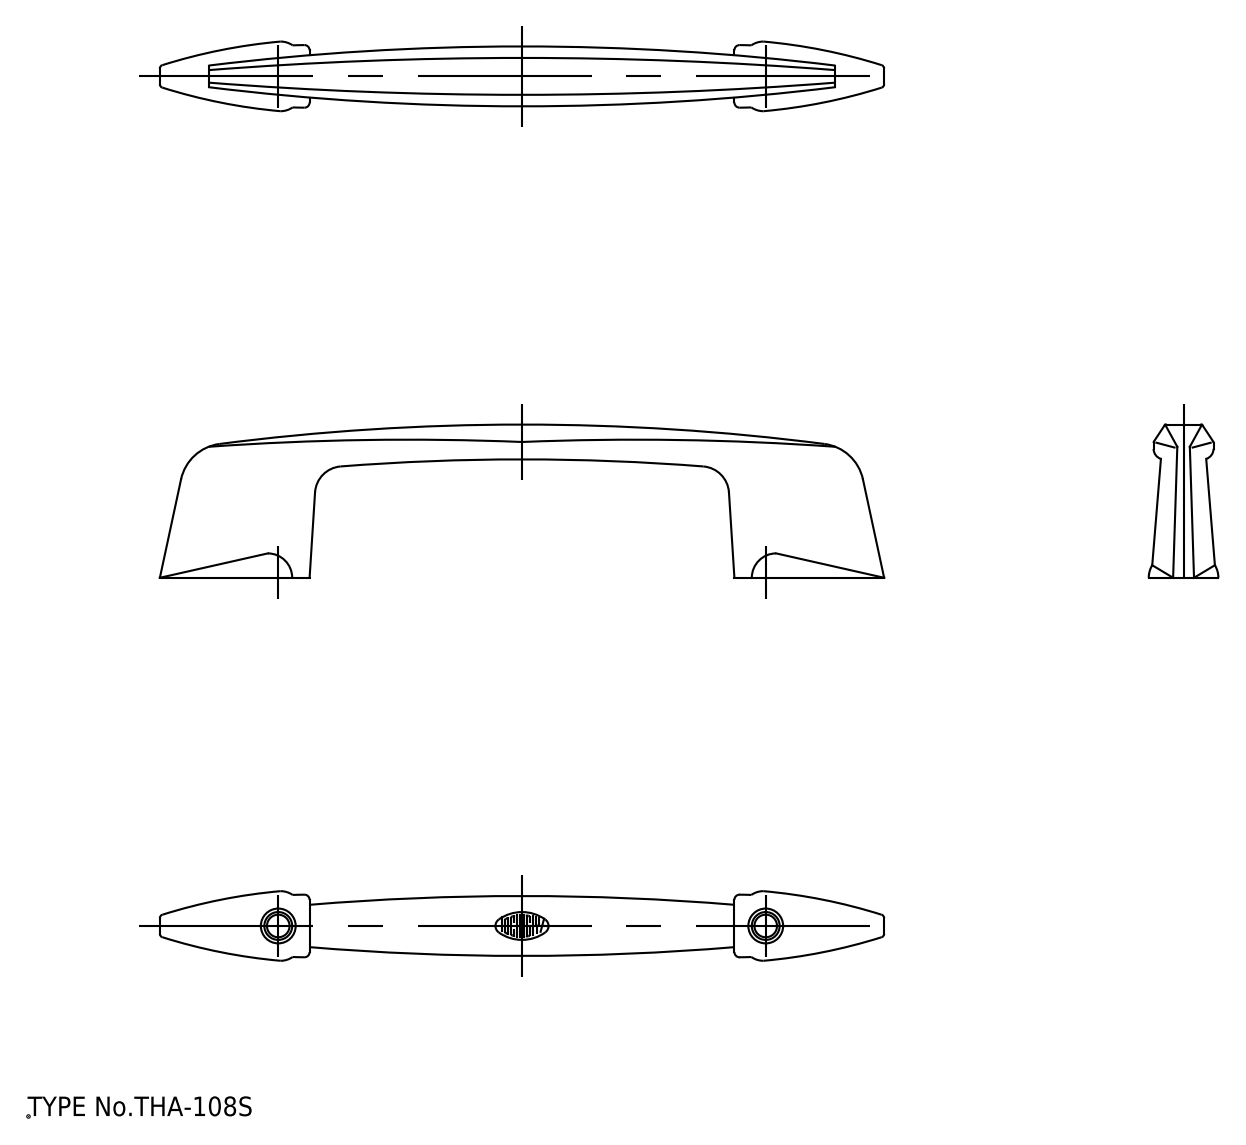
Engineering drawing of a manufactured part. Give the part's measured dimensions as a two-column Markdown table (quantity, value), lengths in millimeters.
| quantity | value |
| --- | --- |
| STEP written by | spGate 19.8.4 (****-****-****-****) (AUTOMOTIVE_DESIGN) |
| units | millimeters |
| bodies | 1 solid, 46 faces (8 planar, 12 cylindrical, 26 other) |
| overall size | 104 × 22 × 10 |
| volume | 6 047 mm³ |
| surface area | 3 941 mm² |
| round holes (diameter × count) | 4 × 2 |
| partial cylindrical surfaces (radius × count) | 4 × 2, 6.5 × 2, 363.85 × 2, 335 × 1, 340 × 1 |
| main face-to-face distances | 12 |
| hole center spacings | 70 |
